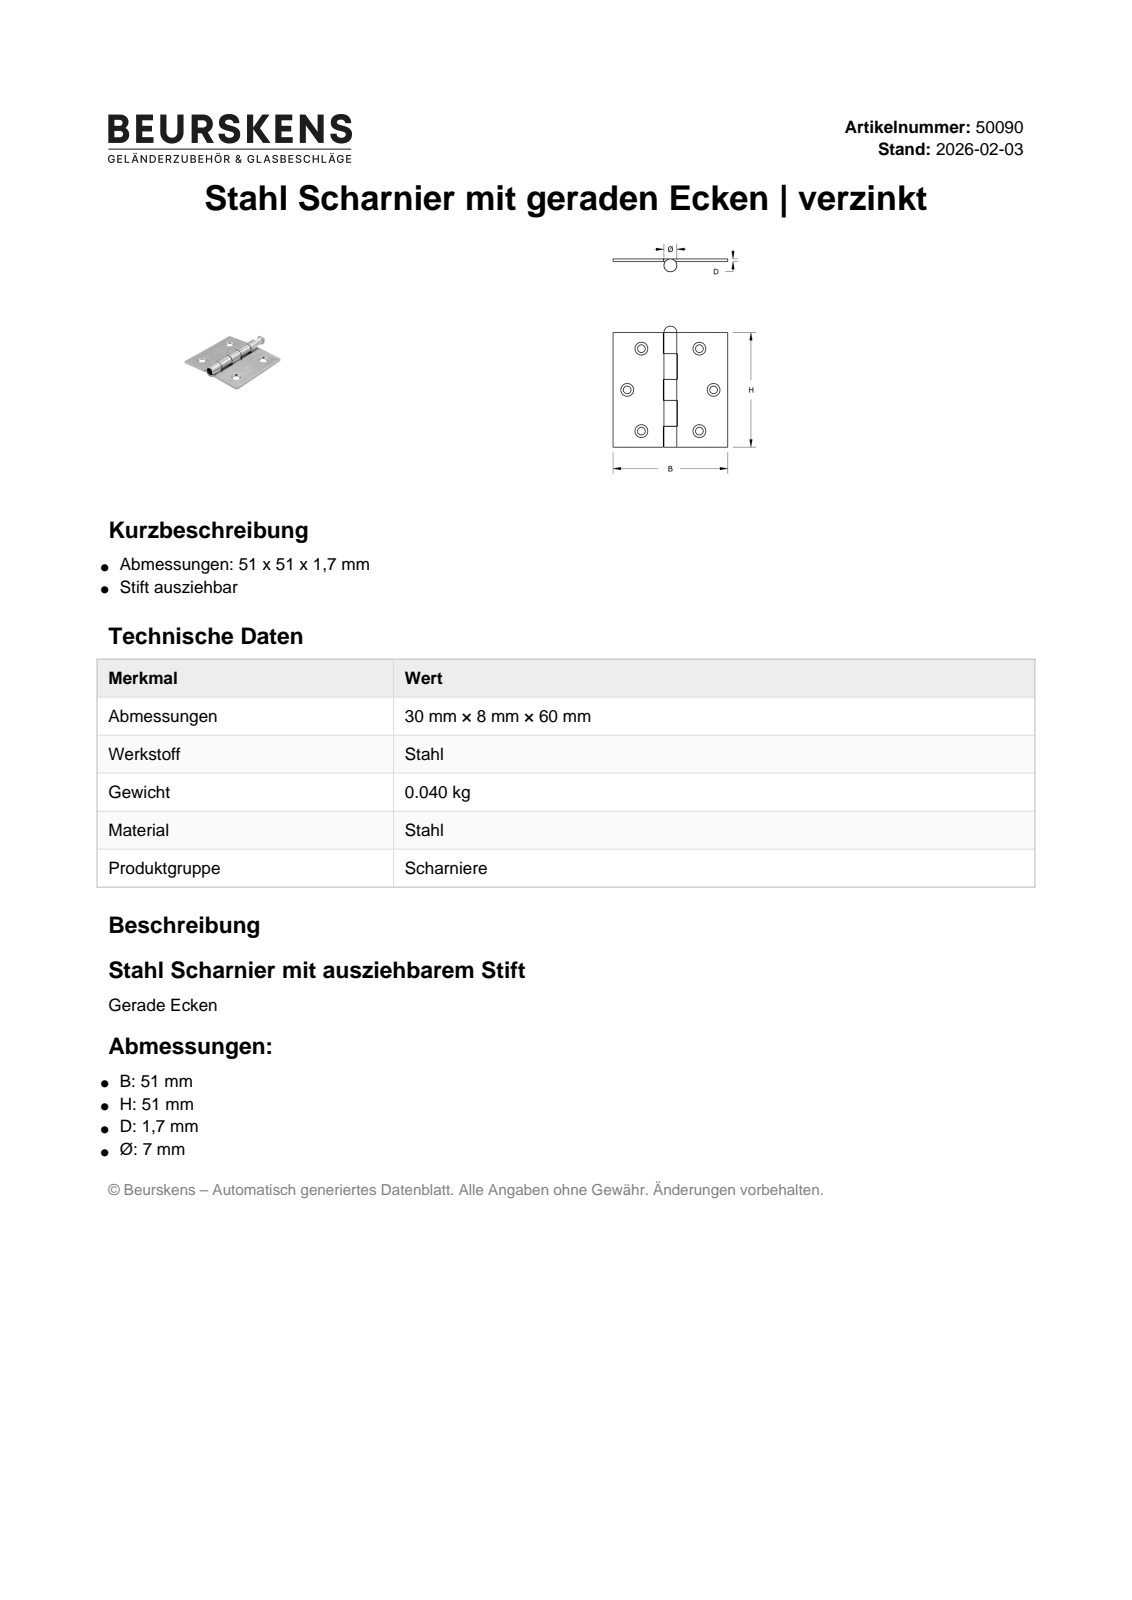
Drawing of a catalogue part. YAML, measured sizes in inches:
part_name: "42020; 42020-01; 42020-02; 42020-03"
step_written_by: "Autodesk Inventor 2023 (AUTOMOTIVE_DESIGN)"
units: inches
bodies: {solids: 3, faces: 46, planar: 26, cylindrical: 15, other: 5}
overall_size: [2.165, 2.008, 0.283]
volume: 0.333
surface_area: 11.88
round_holes:
  - {diameter: 0.197, count: 4}
  - {diameter: 0.161, count: 1}
round_bosses_or_shafts:
  - {diameter: 0.283, count: 1}
  - {diameter: 0.157, count: 1}
face_to_face_distances: [0.059, 2.008, 0.354, 1.654, 0.433, 0.889, 1.119, 0.846, 0.807, 1.201]
hole_center_spacings: [1.22, 1.417, 1.87]
